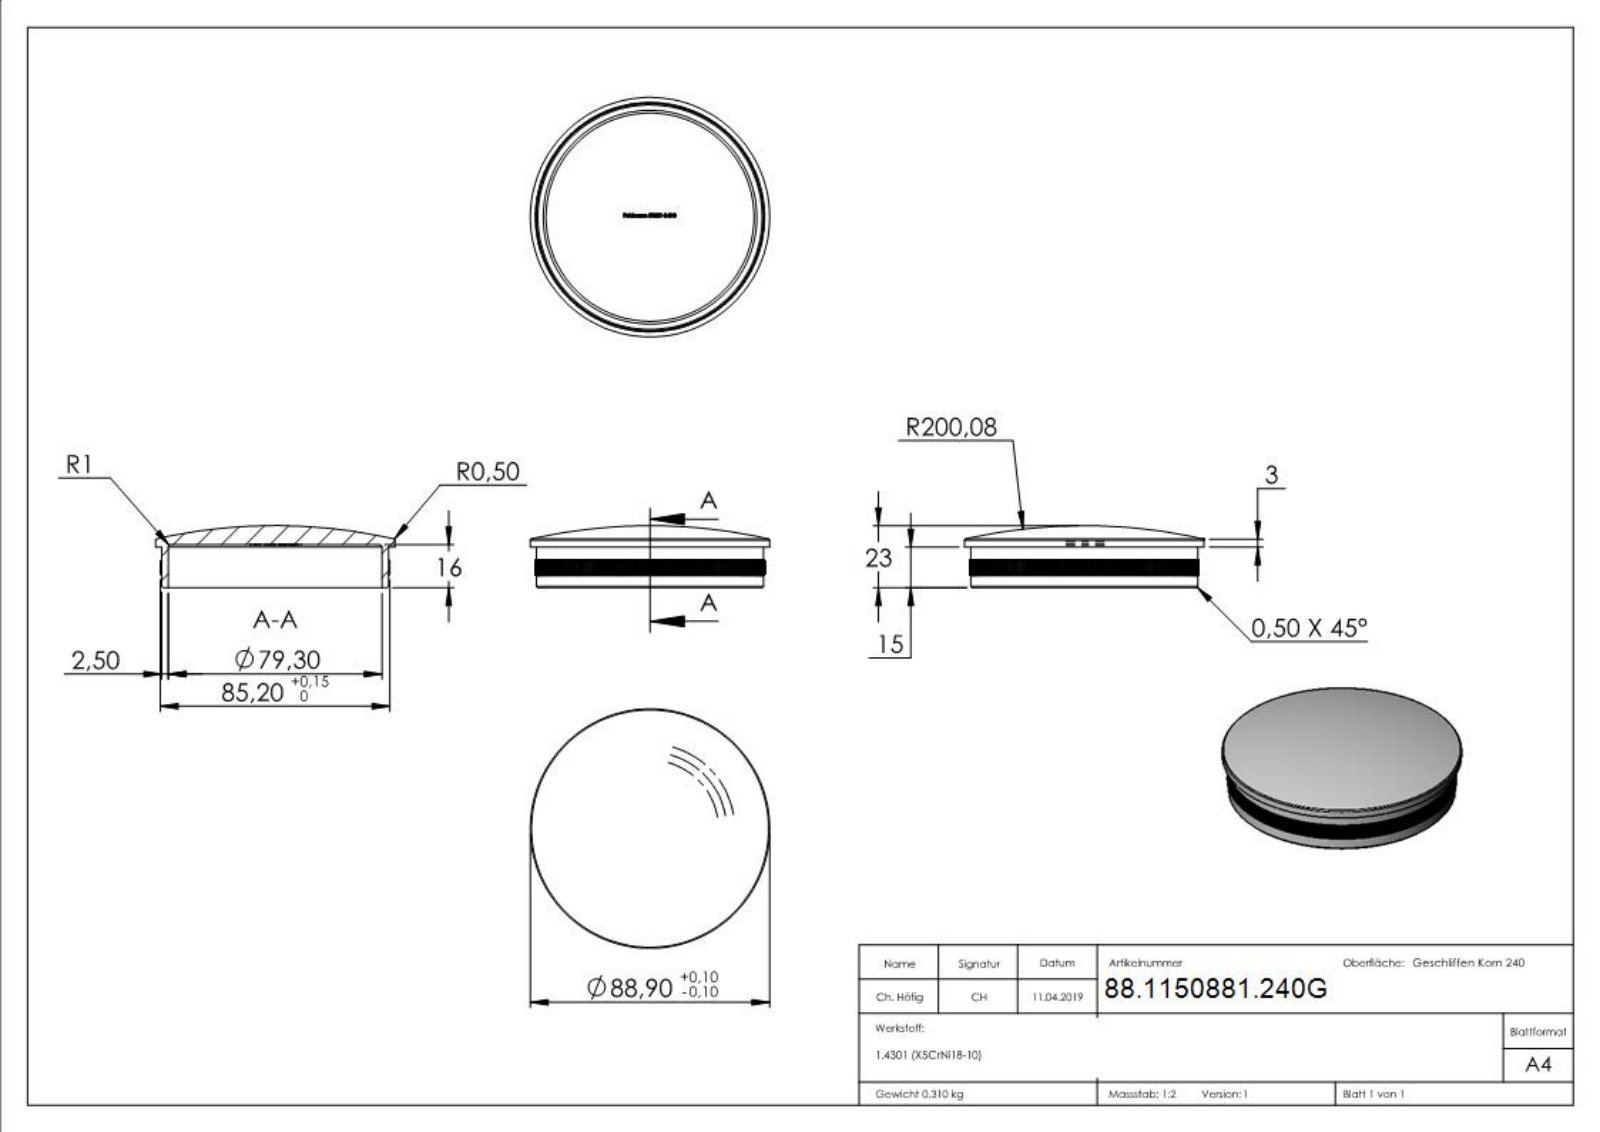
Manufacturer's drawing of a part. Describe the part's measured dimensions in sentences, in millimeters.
The part is named "50881-240G". Its 3-D file was written by "SolidWorks 2015 (CONFIG_CONTROL_DESIGN)". It is 1 solid with 2563 faces: 1044 planar, 468 cylindrical and 1051 other. Overall it measures 88.9 by 88.9 by 23 millimeters. Its volume is 39 282 cubic millimeters and its surface area 22 450 square millimeters. Round holes: 1 of diameter 79.3. Round bosses or shafts: 1 of diameter 88.9, 1 of diameter 84.3. Partial cylindrical surfaces (rounded edges, fillets, slot ends): 1 of radius 42.6. The main face-to-face distances are 1, 15, 16, 42.16, 42.14, 42.12, 42.18, 42.1, 42.2, 16.1.
